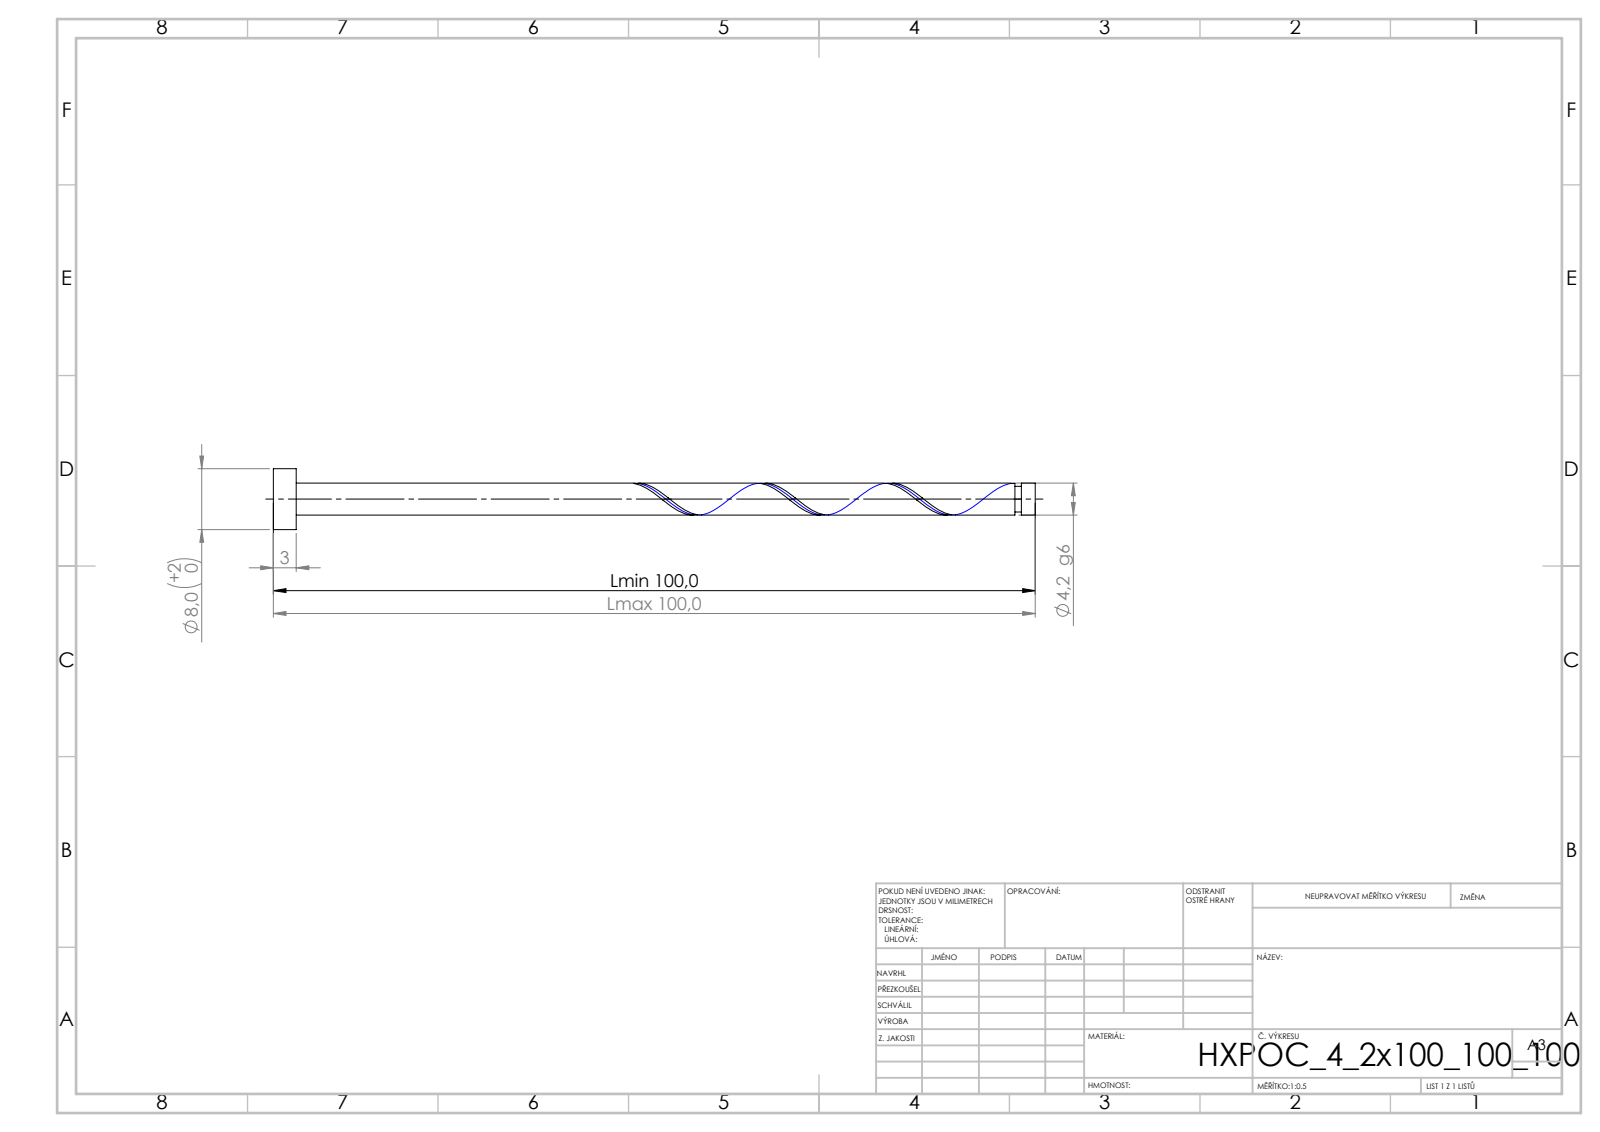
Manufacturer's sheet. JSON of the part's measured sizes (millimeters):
{"step_written_by": "SolidWorks 2019 (CONFIG_CONTROL_DESIGN)", "units": "millimeters", "bodies": {"solids": 1, "faces": 21, "planar": 6, "cylindrical": 14, "other": 1}, "overall_size": [100, 8, 8], "volume_mm3": 1477, "surface_area_mm2": 1491, "round_bosses_or_shafts": [[8, 1], [4.2, 1], [3.36, 1]], "face_to_face_distances": [3, 100, 97, 98.18, 95.18, 1.82, 97.34, 94.34, 0.84, 2.66]}
